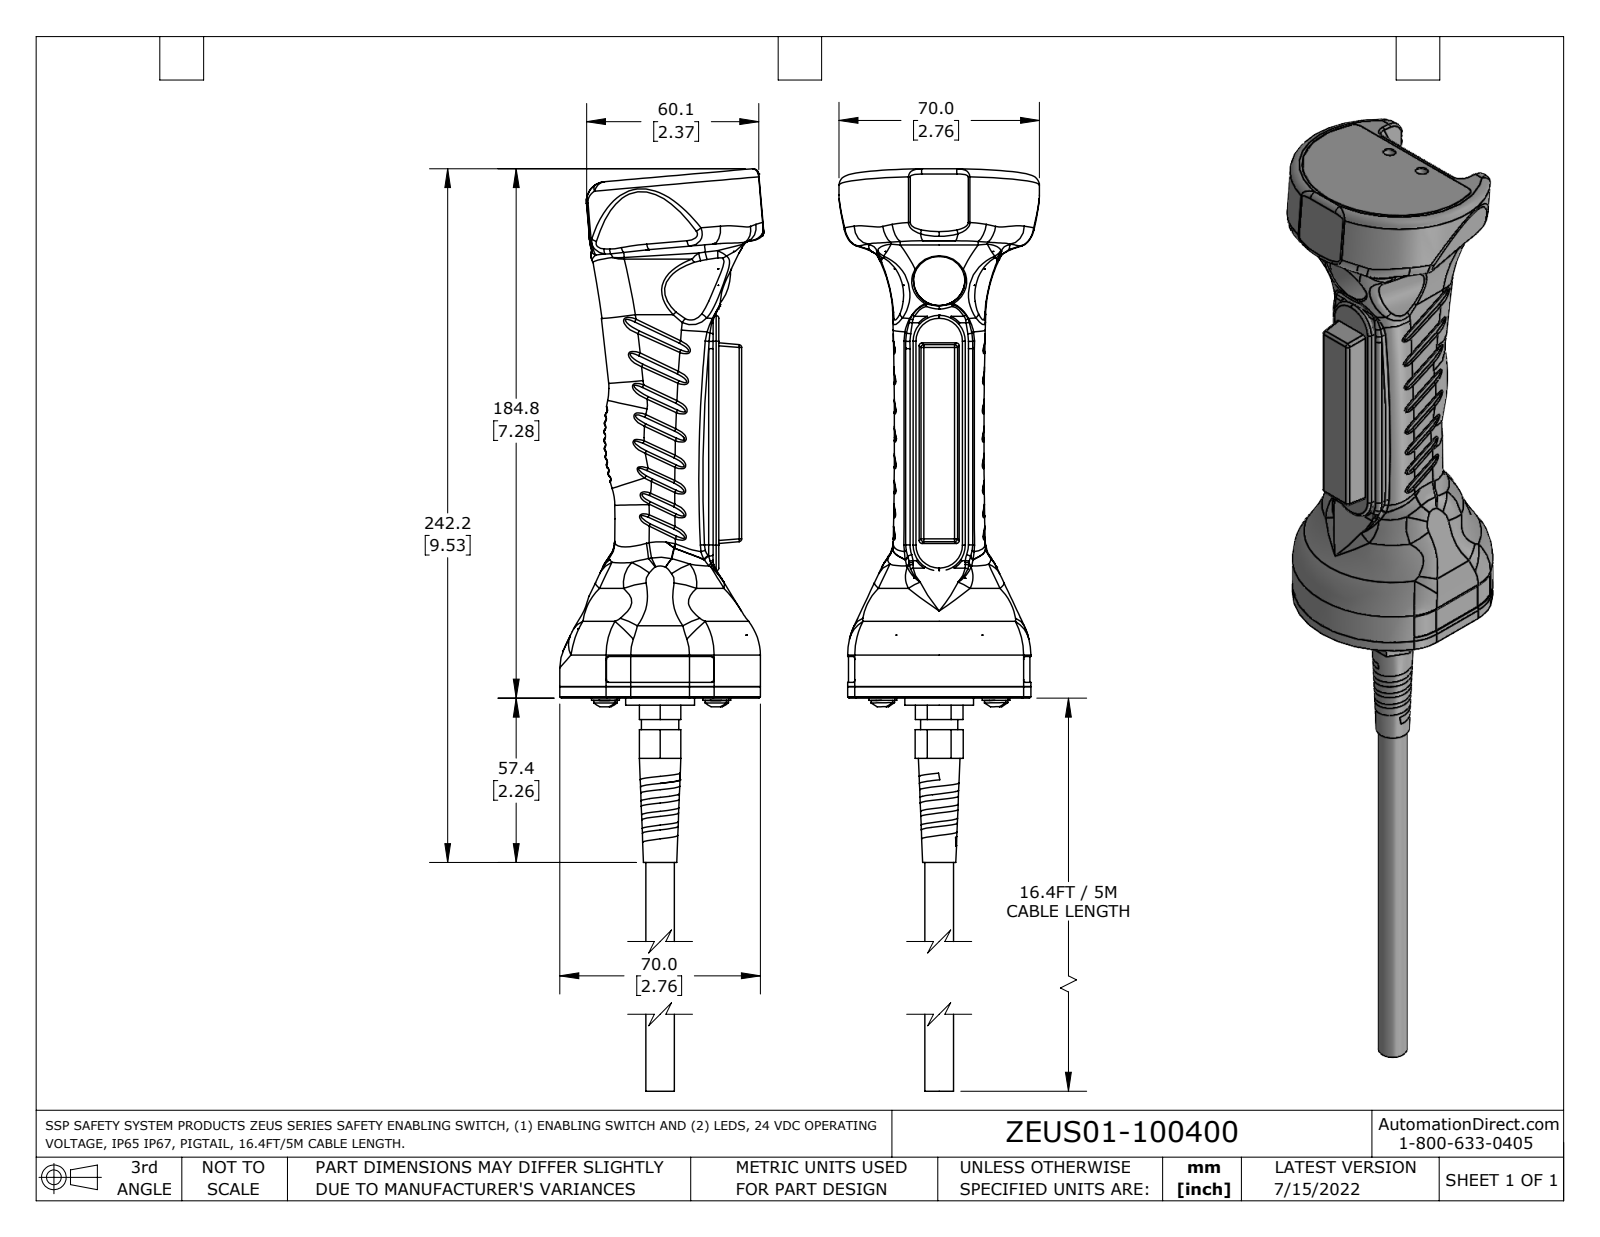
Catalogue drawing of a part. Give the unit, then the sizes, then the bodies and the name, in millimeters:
Units: millimetres
Overall size (bounding box): 379.1 × 71.2 × 70
Round holes (diameter × count): ⌀3.4 ×4, ⌀4.3 ×4, ⌀4.5 ×4, ⌀5 ×4, ⌀2.5 ×2, ⌀2.8 ×2, ⌀4.2 ×2, ⌀4.4 ×2, ⌀8.4 ×2, ⌀10 ×1, ⌀10.6 ×1, ⌀14 ×1
Round bosses / shafts (diameter × count): ⌀9 ×4, ⌀7.5 ×4, ⌀4 ×4, ⌀1 ×4, ⌀6 ×2, ⌀24 ×1, ⌀21 ×1, ⌀19.7 ×1
Partial cylindrical surfaces — rounded edges, fillets, slot ends (radius × count): R0.1 ×96, R1 ×51, R0.7 ×48, R2 ×21, R3 ×10, R0.8 ×7, R0.3 ×5, R15.7 ×4
Main face-to-face distances: 4, 2, 1.7, 0.4, 1.5, 0.5, 2.5, 4.5, 2, 14.5
Hole centre spacings: 38.9, 16, 22, 30, 39.6, 55.5, 10.3, 10.3
Volume: 388 900 mm³ · Surface area: 81 230 mm²
Bodies: 16 solids, 1142 faces (321 planar, 399 cylindrical, 422 other)
Part name (STEP PRODUCT): ZEUS01-100400
STEP written by: SolidWorks 2021 (AUTOMOTIVE_DESIGN)
